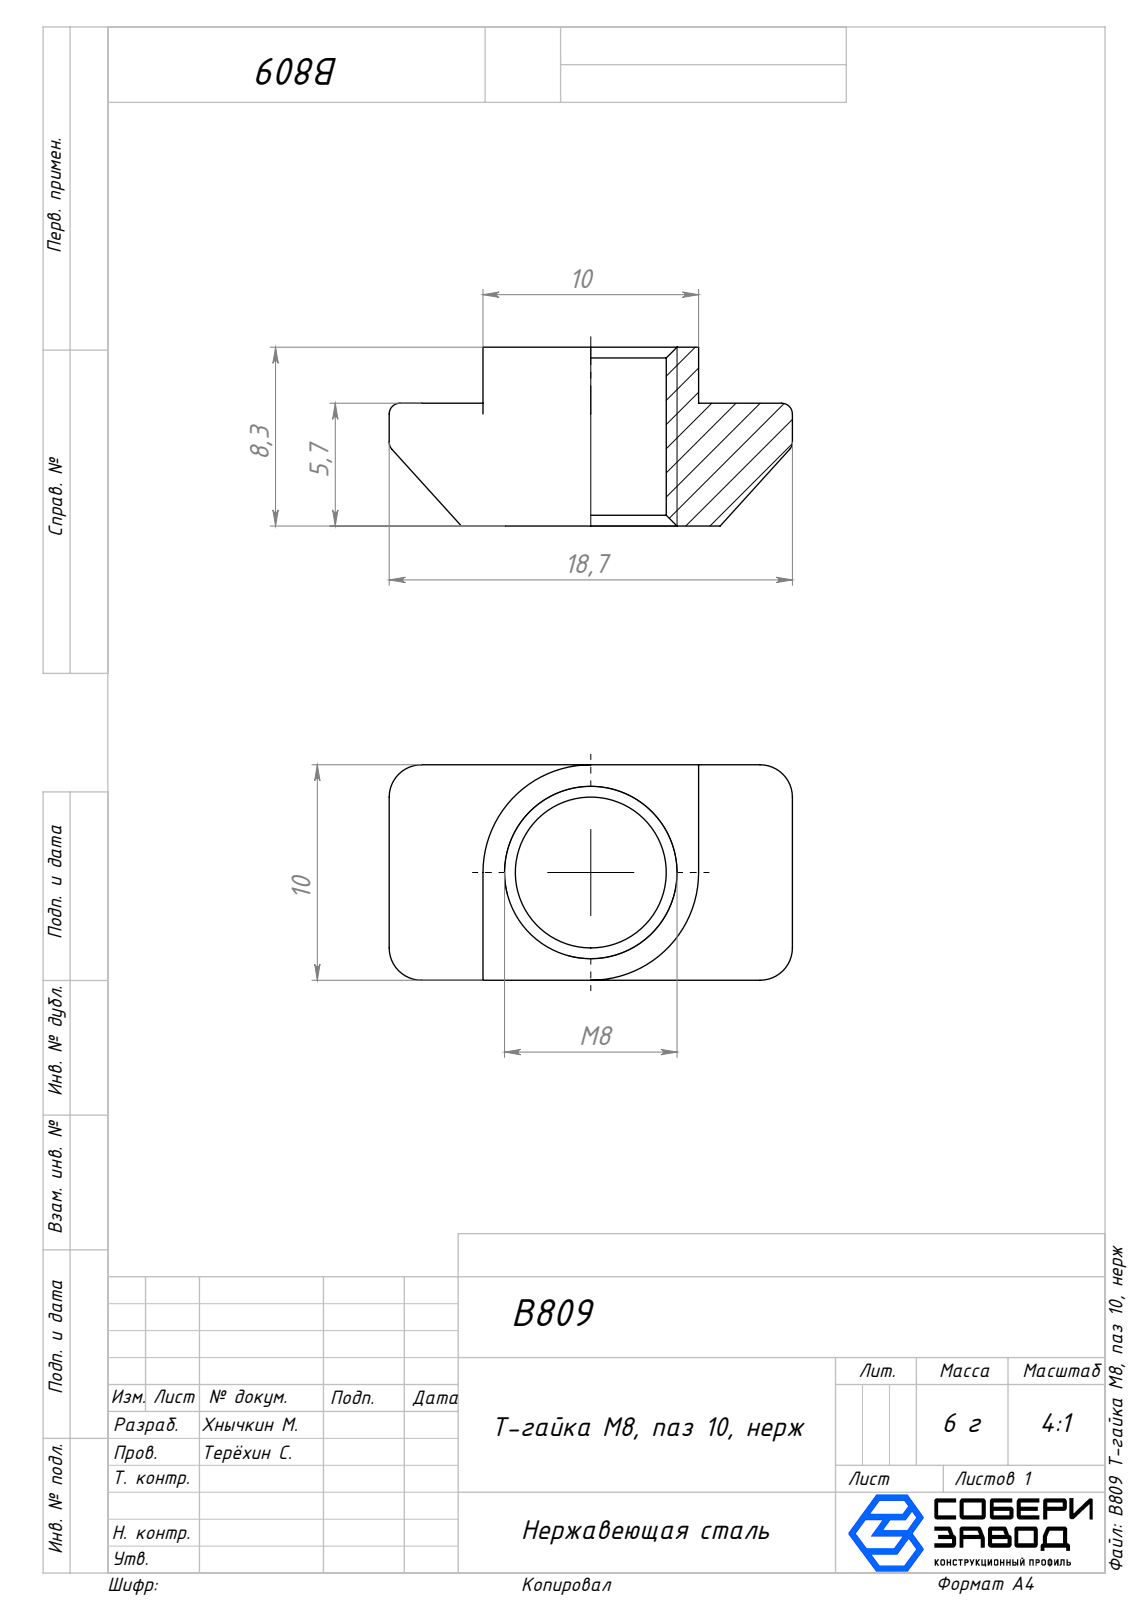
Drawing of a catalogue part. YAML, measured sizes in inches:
part_name: "B809 Т-гайка М8, паз 10, нерж"
step_written_by: "SolidWorks 2025 (AUTOMOTIVE_DESIGN)"
units: inches
bodies: {solids: 1, faces: 44, planar: 12, cylindrical: 20, other: 12}
overall_size: [0.736, 0.394, 0.327]
volume: 0.051
surface_area: 1.22
round_holes:
  - {diameter: 0.276, count: 1}
partial_cylinders:
  - {radius: 0.059, count: 8}
  - {radius: 0.02, count: 6}
  - {radius: 0.197, count: 1}
face_to_face_distances: [0.394, 0.224, 0.327, 0.102, 0.171, 0.565, 0.736]
